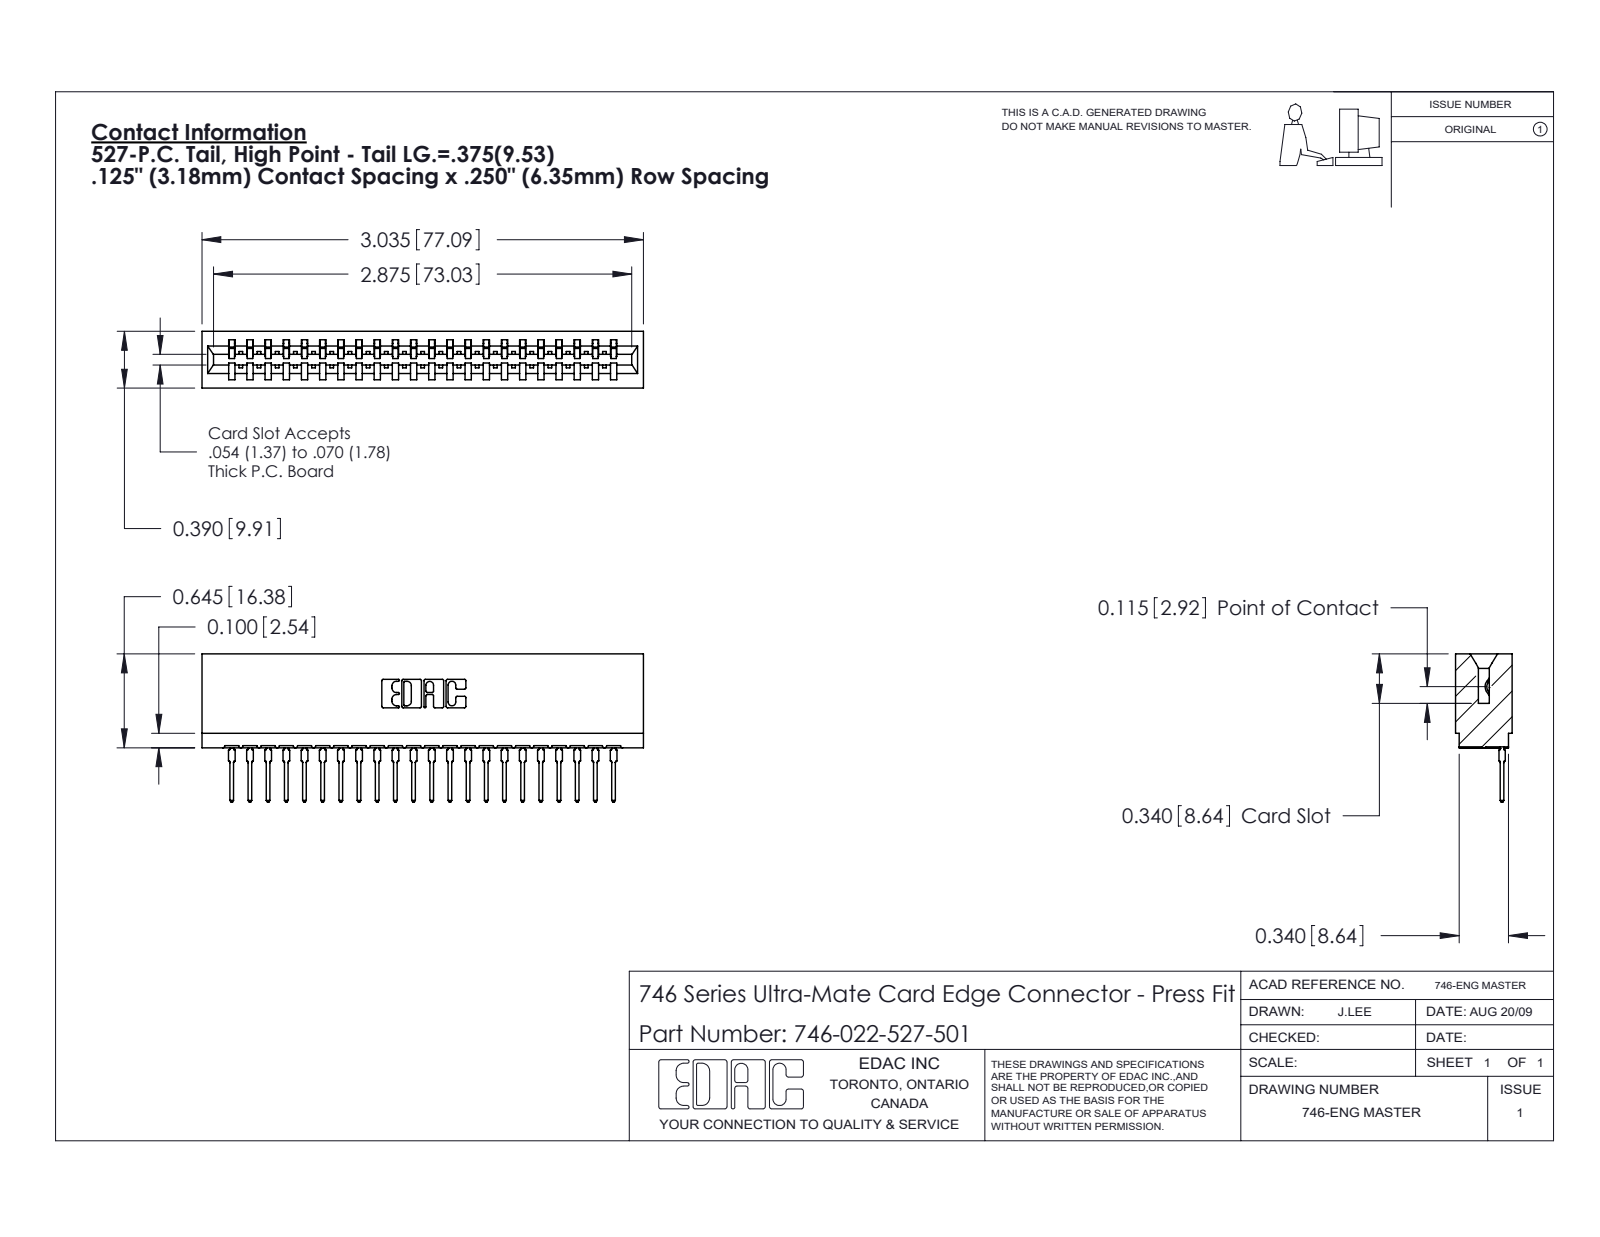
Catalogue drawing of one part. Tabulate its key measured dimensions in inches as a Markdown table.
| quantity | value |
| --- | --- |
| part name | 746-022-527-501; 746-292-001_527; 746 Part_.340 Slot Depth - 01 |
| STEP written by | SolidWorks 2020 (CONFIG_CONTROL_DESIGN) |
| units | inches |
| bodies | 23 solids, 2473 faces (1441 planar, 460 cylindrical, 572 other) |
| overall size | 3.035 × 1.019 × 0.39 |
| volume | 0.537 in³ |
| surface area | 18.11 in² |
| partial cylindrical surfaces (radius × count) | 0.021 × 44, 0.015 × 23, 0.01 × 22, 0.007 × 6, 0.031 × 6, 0.005 × 4, 0.011 × 4, 0.026 × 3 |
| main face-to-face distances | 0.057, 0.25, 0.333, 0.39, 0.025, 0.307, 0.125, 0.375, 0.125, 0.5 |
